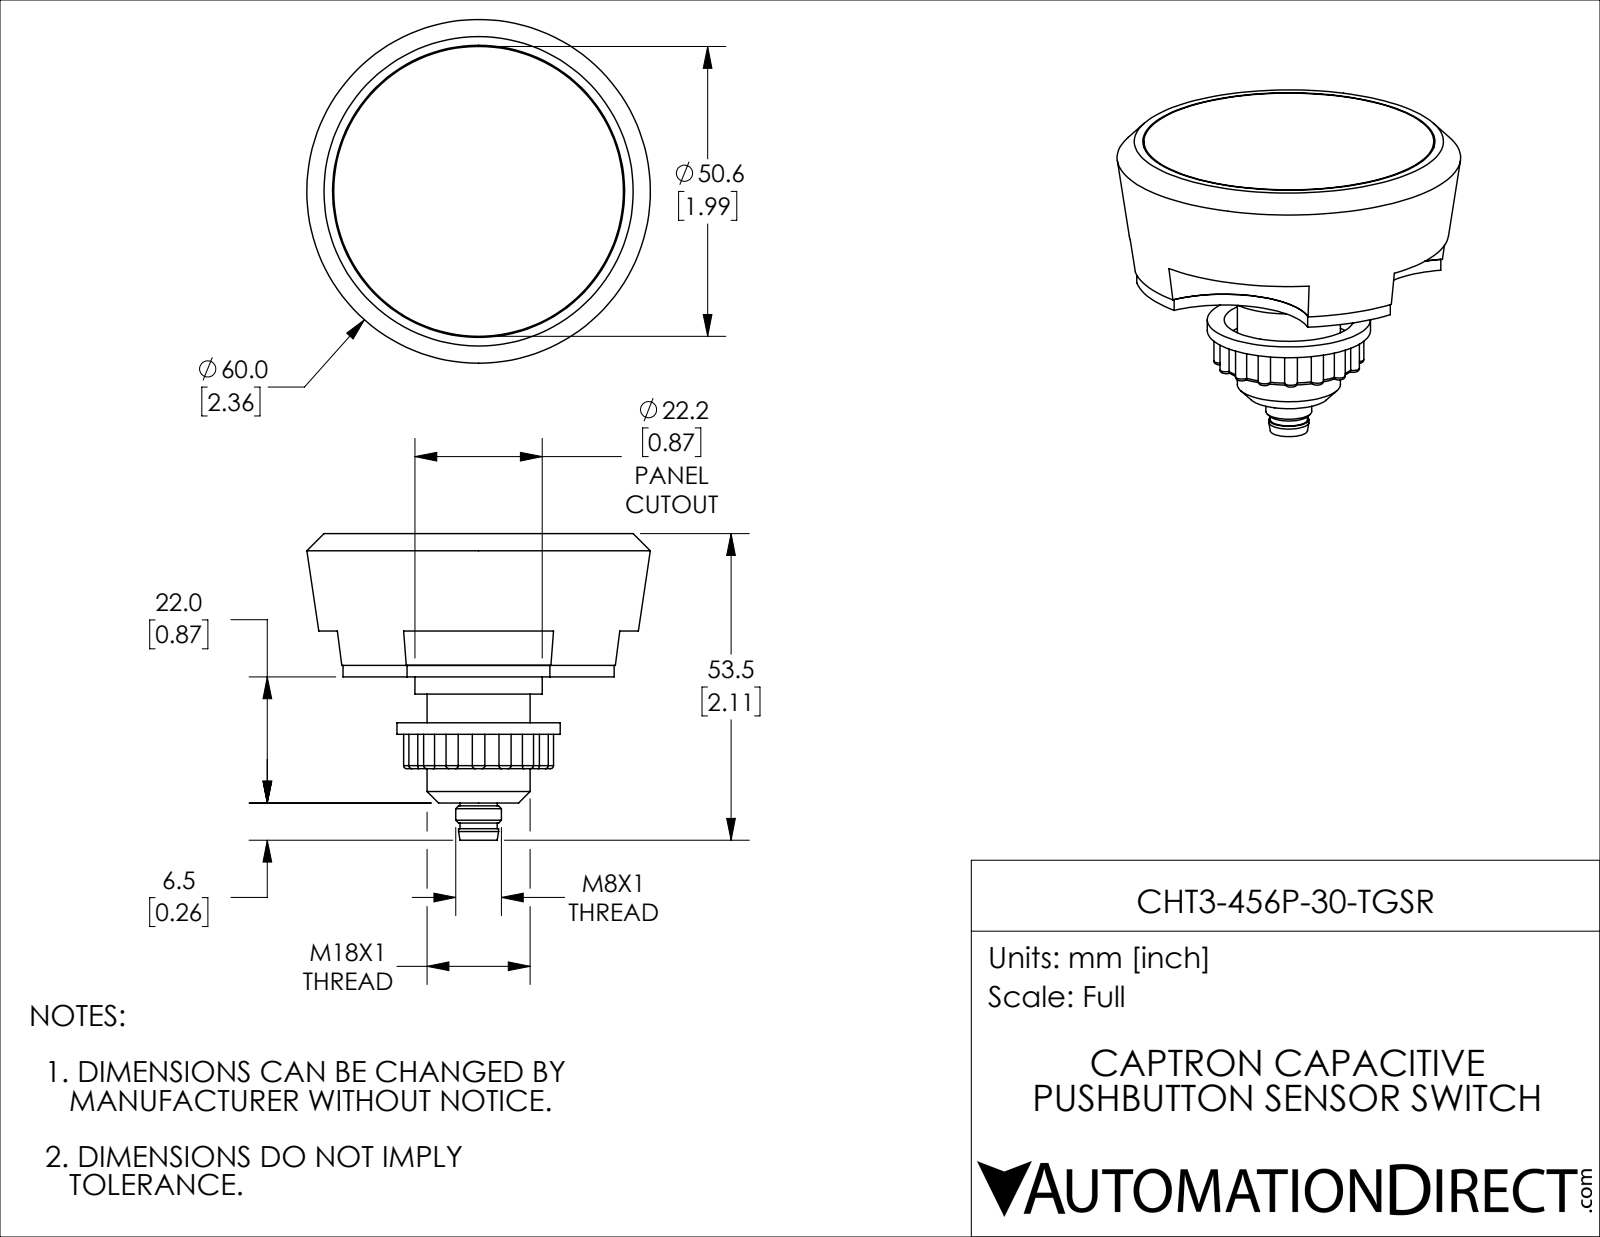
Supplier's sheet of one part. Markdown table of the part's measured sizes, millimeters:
| quantity | value |
| --- | --- |
| part name | CHT3-456P-30-TGSR |
| STEP written by | SolidWorks 2019 (CONFIG_CONTROL_DESIGN) |
| units | millimeters |
| bodies | 9 solids, 197 faces (27 planar, 95 cylindrical, 75 other) |
| overall size | 60 × 60 × 53.5 |
| volume | 63 958 mm³ |
| surface area | 20 586 mm² |
| round holes (diameter × count) | 6 × 1, 17 × 1, 22.6 × 1, 51 × 1 |
| round bosses / shafts (diameter × count) | 1 × 4, 50.6 × 1, 28.5 × 1, 22.2 × 1, 18 × 1, 8 × 1, 7 × 1, 6.5 × 1 |
| partial cylindrical surfaces (radius × count) | 1.1 × 16, 15 × 4, 12 × 1, 26.75 × 1 |
| main face-to-face distances | 23, 20.2, 2.8, 0.5, 20.7, 2.3, 2, 8, 22.2, 22.7 |
